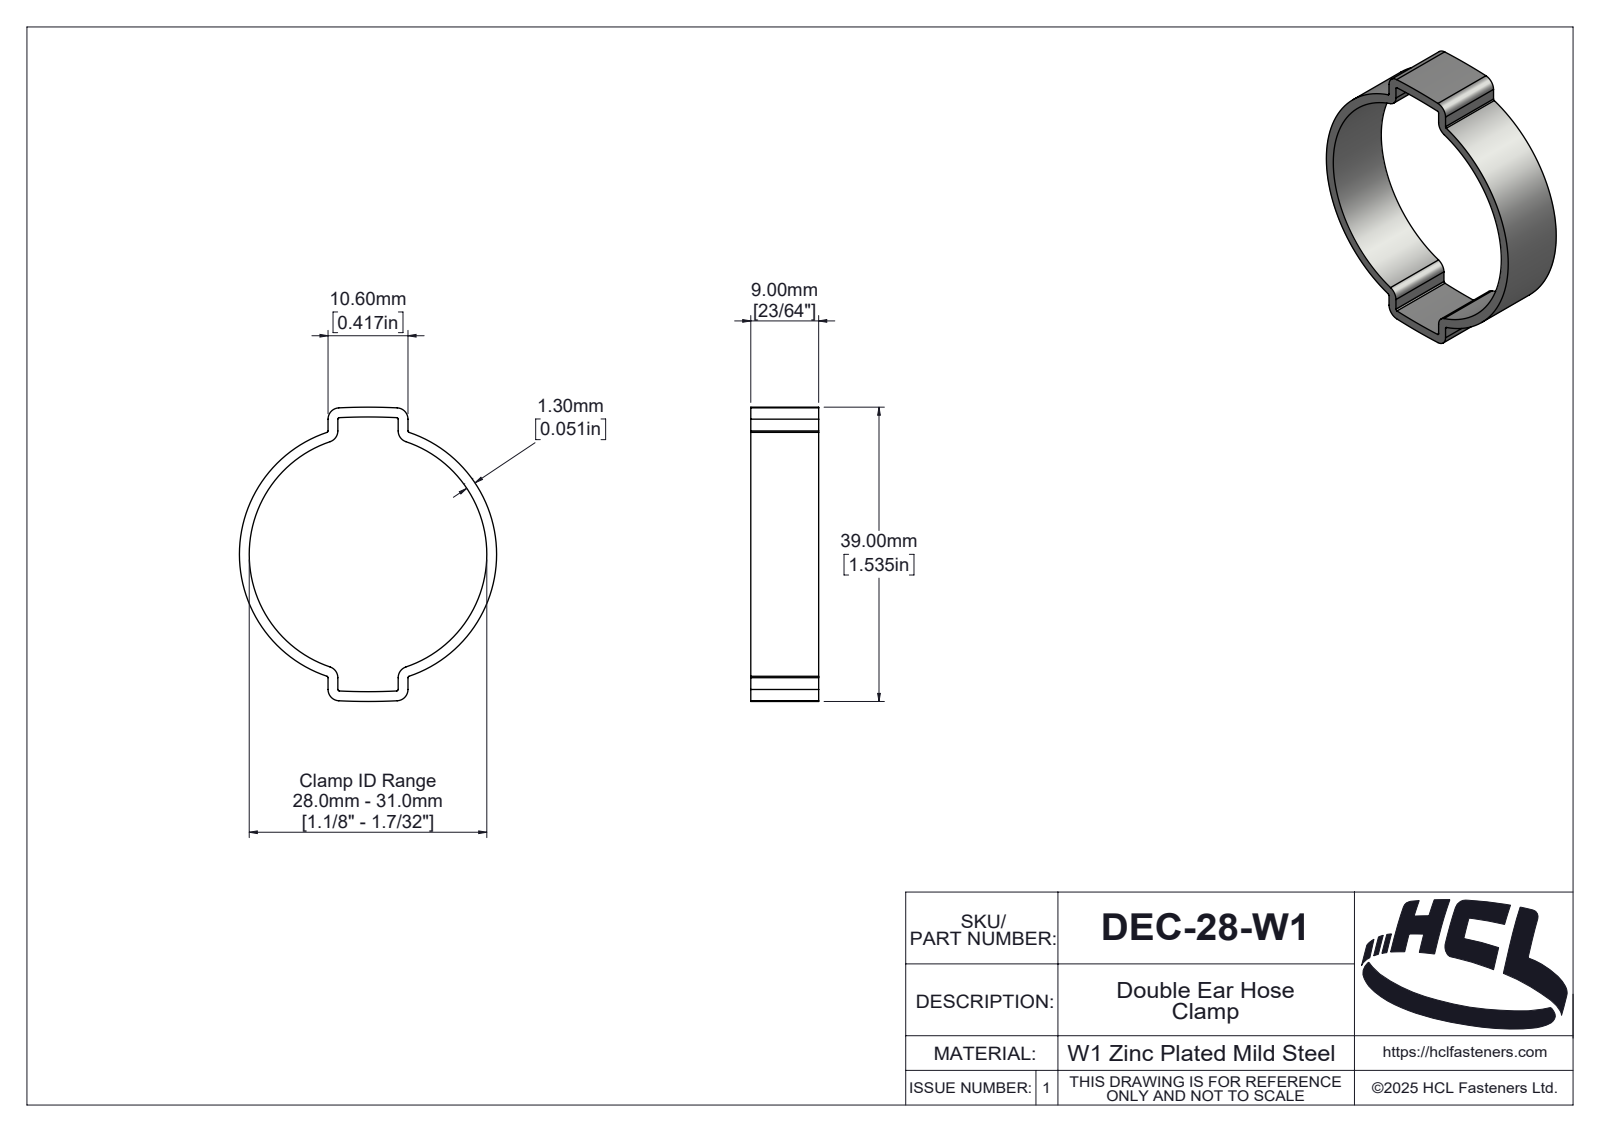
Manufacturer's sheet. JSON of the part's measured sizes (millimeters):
{"part_name": "DEC-28-W1", "step_written_by": "SolidWorks 2025 (AUTOMOTIVE_DESIGN)", "units": "millimeters", "bodies": {"solids": 1, "faces": 137, "planar": 12, "cylindrical": 67, "other": 58}, "overall_size": [39, 34.1, 9], "volume_mm3": 1319, "surface_area_mm2": 2328, "partial_cylinders_radius": [[0.2, 8], [1.5, 8], [80.05, 2], [81.35, 2], [0.28, 1], [1.13, 1], [1.41, 1], [1.49, 1]], "face_to_face_distances": [9, 1.3, 9.3, 10.6, 8, 5.14, 3.84, 4.16, 5.46, 4.93]}
